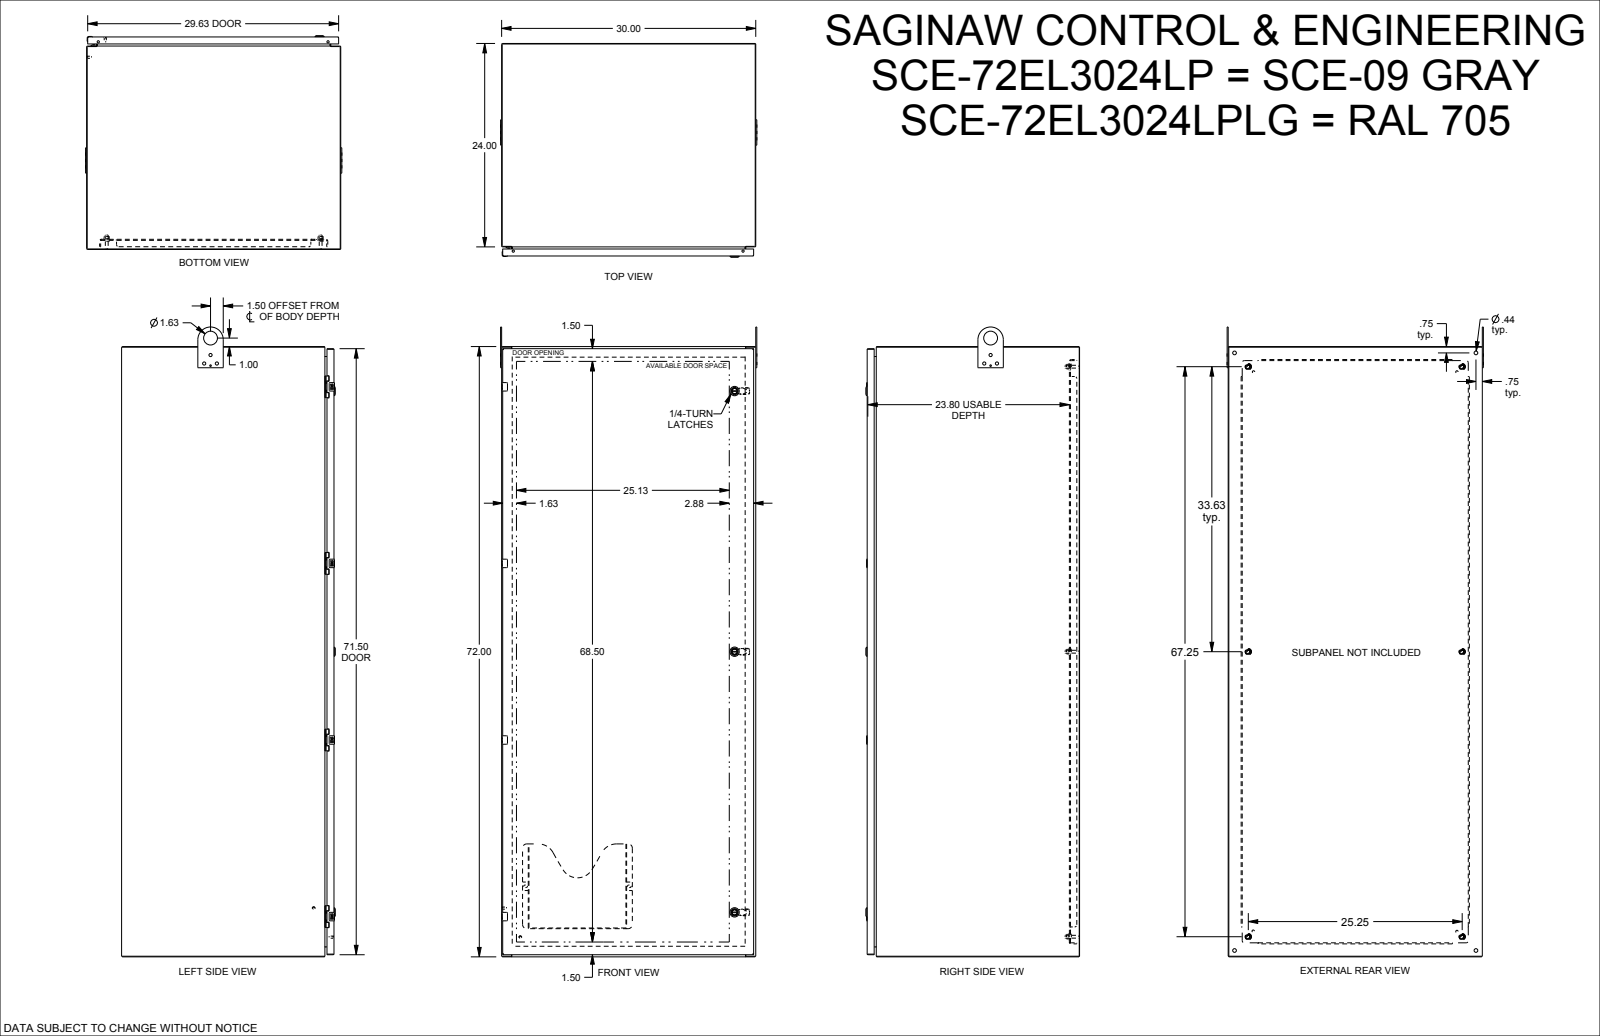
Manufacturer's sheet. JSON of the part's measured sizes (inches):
{"part_name": "SCE-72EL3024LP", "step_written_by": "SolidWorks 2019 (CONFIG_CONTROL_DESIGN)", "units": "inches", "bodies": {"solids": 0, "faces": 4639, "planar": 2133, "cylindrical": 1308, "other": 1198}, "overall_size": [74.31, 30.262, 25.23], "round_holes": [[0.266, 10], [0.172, 8], [0.205, 8], [0.244, 8], [0.375, 8], [0.367, 6], [0.5, 6], [0.04, 4], [0.156, 4], [0.218, 4], [0.281, 4], [0.437, 4]], "round_bosses_or_shafts": [[0.17, 12], [0.25, 8], [0.24, 8], [0.366, 6], [0.332, 6], [0.196, 5], [0.248, 4], [1.102, 3]], "partial_cylinders_radius": [[0.012, 82], [0.01, 58], [0.015, 42], [0.02, 28], [0.03, 25], [0.025, 20], [0.1, 20], [0.031, 18]], "face_to_face_distances": [0.075, 29.925, 0.075, 24.923, 24.998, 25.073, 24.998, 0.125, 1.2, 23.873], "hole_center_spacings": [20.833, 41.667, 20.833, 0.985, 62.5, 0.02, 0.493, 0.494]}
